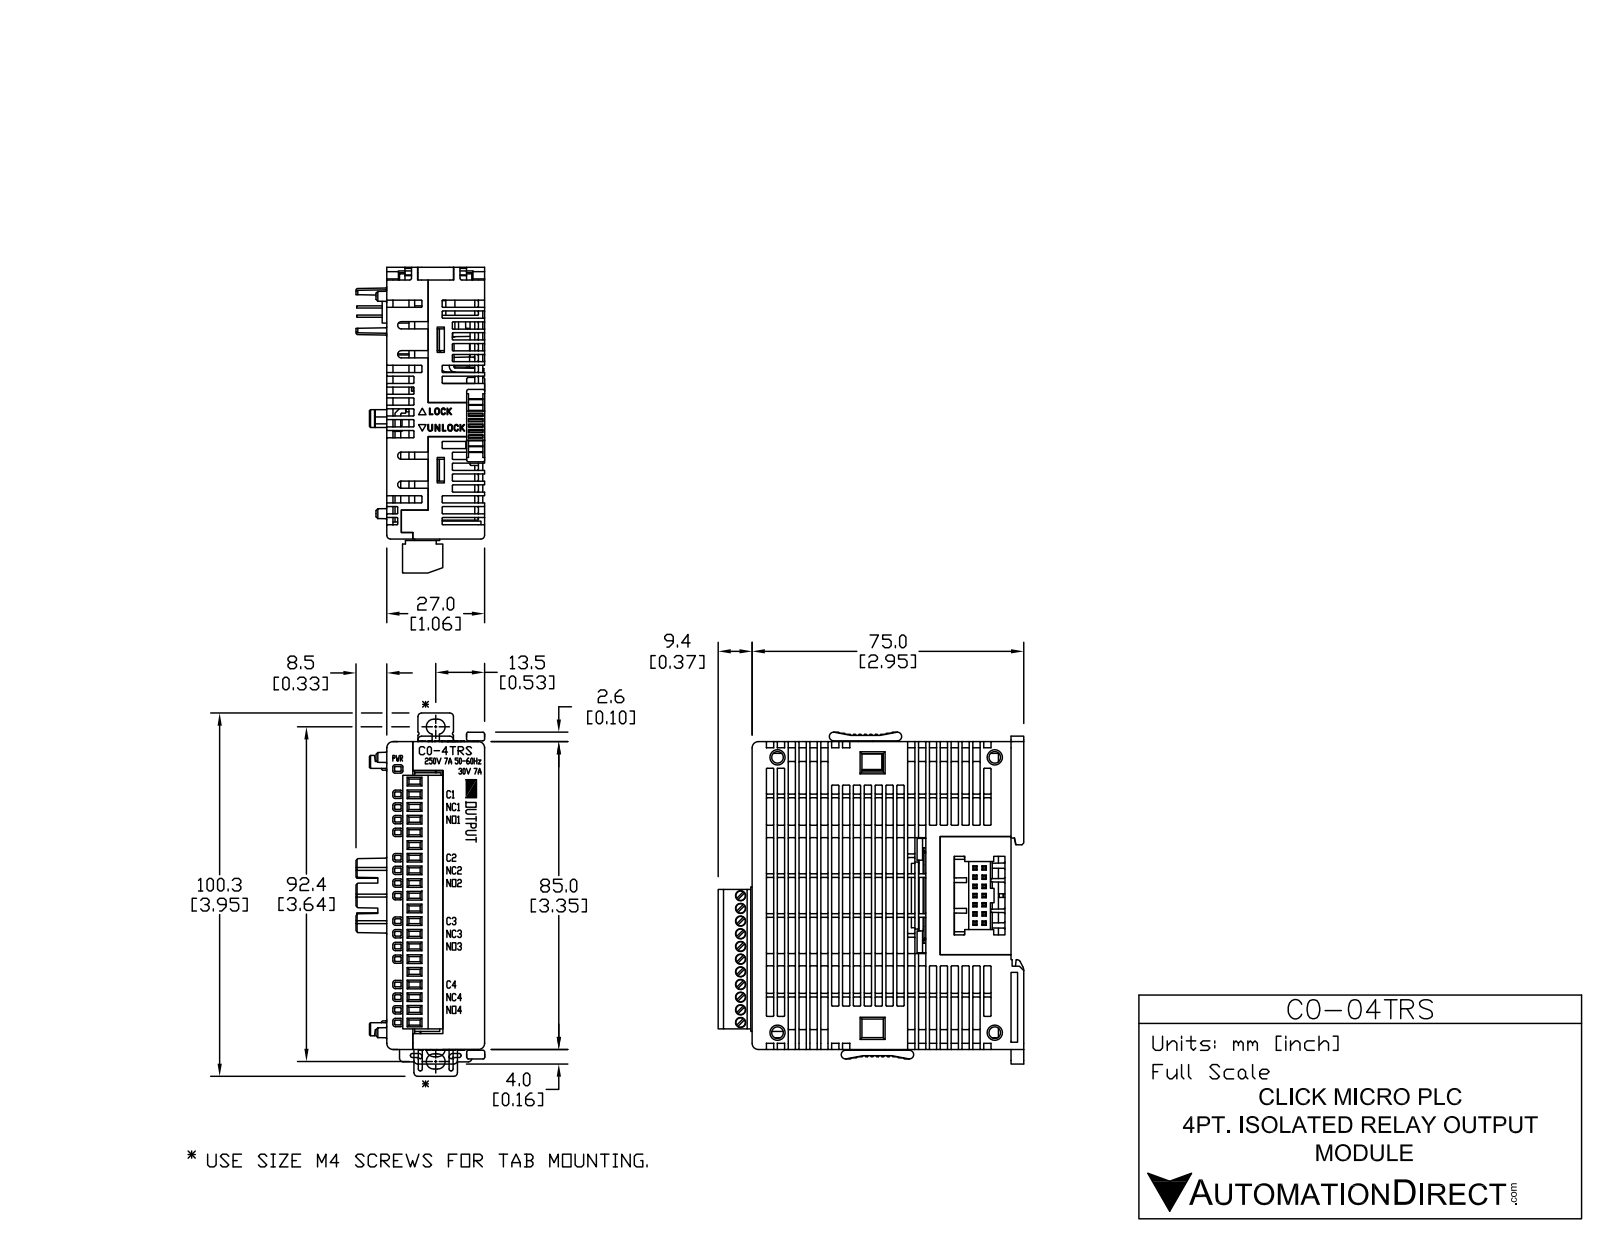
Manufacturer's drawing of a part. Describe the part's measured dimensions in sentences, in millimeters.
The part is named "C0-04TRS". Its 3-D file was written by "SolidWorks 2009 (AUTOMOTIVE_DESIGN)". It is 1 solid with 3989 faces: 2836 planar, 1037 cylindrical and 116 other. Overall it measures 91.6 by 84.4 by 35.55 millimeters. Its volume is 165 090 cubic millimeters and its surface area 33 615 square millimeters. Round holes: 20 of diameter 1, 20 of diameter 2.8, 4 of diameter 3.2, 2 of diameter 2. Round bosses or shafts: 20 of diameter 2.6, 1 of diameter 1.9. Partial cylindrical surfaces (rounded edges, fillets, slot ends): 570 of radius 0.2, 43 of radius 0.5, 22 of radius 0.3, 20 of radius 2.8, 18 of radius 1, 12 of radius 1.2, 6 of radius 1.7, 4 of radius 2.1. The main face-to-face distances are 0.5, 27.01, 0.51, 26.5, 71.5, 85, 1.7, 26.3, 26.81, 3.5. The hole center spacings are 3.5, 7, 10.5, 14, 17.5, 21, 24.5, 28.
